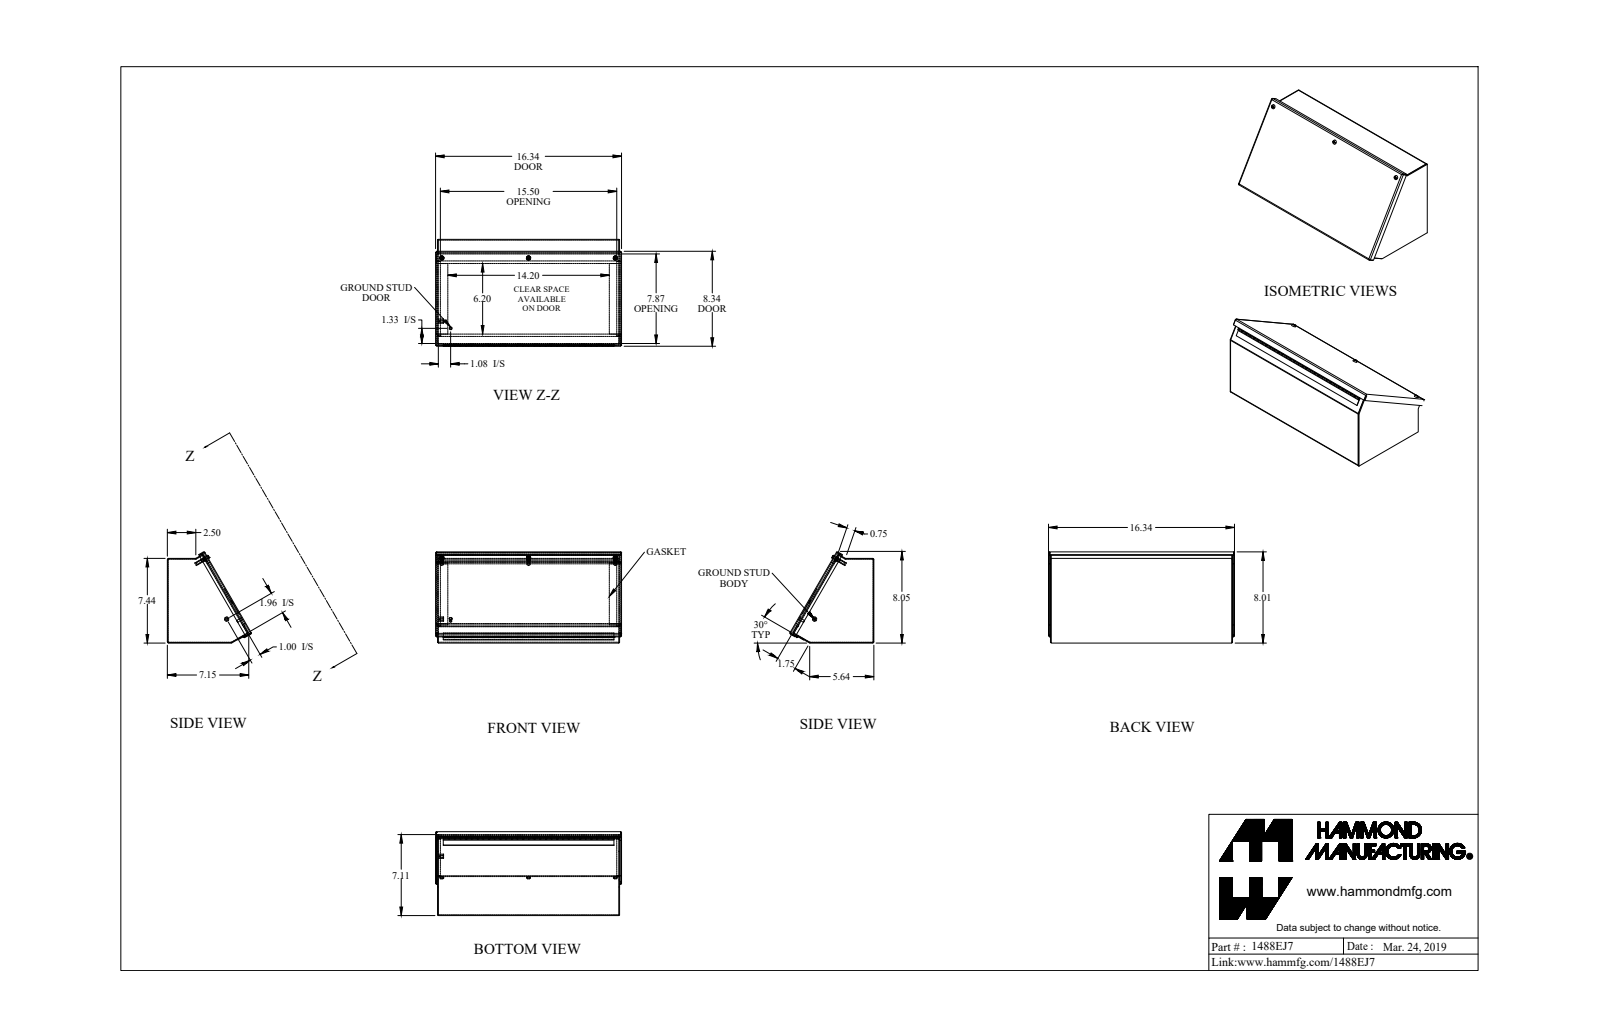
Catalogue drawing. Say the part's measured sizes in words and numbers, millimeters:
The part is named "1488EJ7_Default". Its 3-D file was written by "SolidWorks 2019 (CONFIG_CONTROL_DESIGN)". It is 22 solids with 638 faces: 381 planar, 221 cylindrical and 36 other. Overall it measures 415.1 by 203.4 by 187.3 millimeters. Its volume is 839 200 cubic millimeters and its surface area 816 800 square millimeters. Round holes: 3 of diameter 4, 3 of diameter 6.4, 1 of diameter 1.3, 1 of diameter 4. Round bosses or shafts: 3 of diameter 9.9, 3 of diameter 7, 3 of diameter 4.8, 3 of diameter 3.8, 1 of diameter 9.5, 1 of diameter 6.4, 1 of diameter 4.8, 1 of diameter 2.5. Partial cylindrical surfaces (rounded edges, fillets, slot ends): 12 of radius 0.9, 12 of radius 2.7, 3 of radius 3.2, 3 of radius 4.1, 3 of radius 4.3, 1 of radius 1.4, 1 of radius 1.4. The main face-to-face distances are 1.8, 1.8, 404.6, 187.1, 6.4, 8.2, 402.7, 406.4, 188.9, 185.2. The hole center spacings are 193.7, 193.7, 387.4, 387.4, 56.5.
